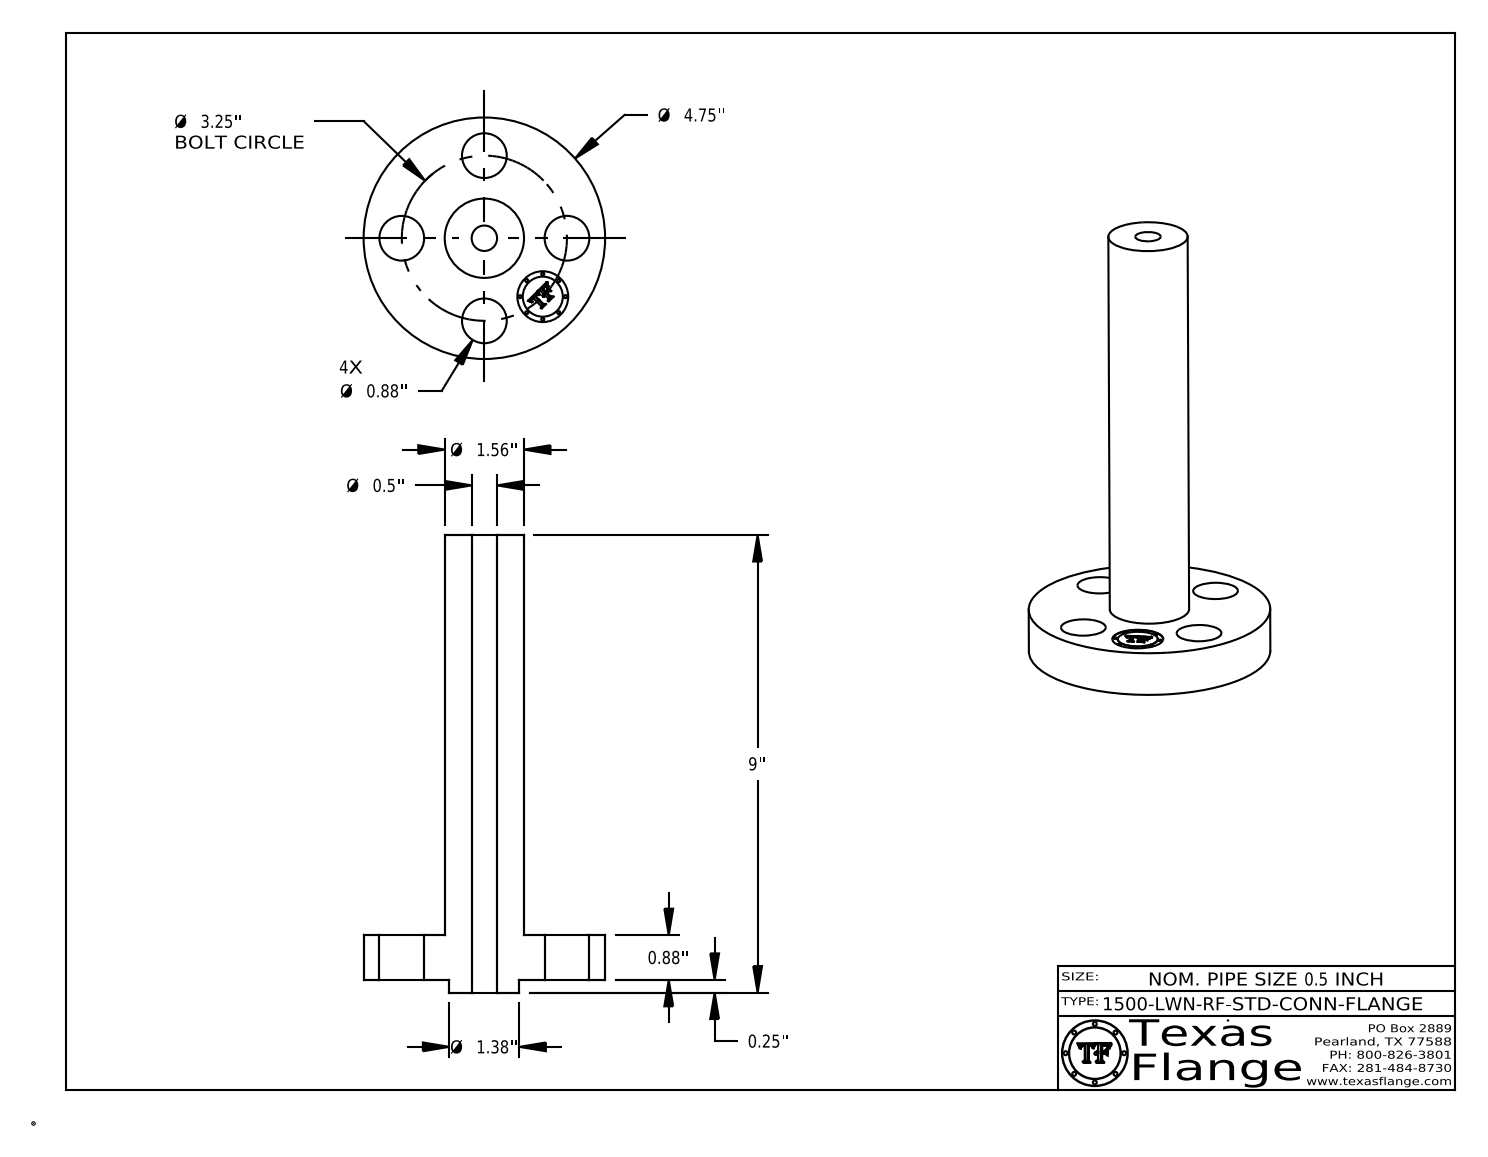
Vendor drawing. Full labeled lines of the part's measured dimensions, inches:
Part name (STEP PRODUCT): 0.5-1500-LWN-RF-STD-CONN-FLANGE
STEP written by: CATIA V5 STEP AP214 (AUTOMOTIVE_DESIGN)
Units: inches
Bodies: 1 solid, 405 faces (369 planar, 36 cylindrical, 0 other)
Overall size (bounding box): 9 × 4.75 × 4.75
Volume: 27.1 in³ · Surface area: 106.9 in²
Round holes (diameter × count): ⌀0.88 ×4, ⌀0.5 ×1, ⌀1 ×1
Round bosses / shafts (diameter × count): ⌀0.061 ×8, ⌀4.75 ×1, ⌀1.56 ×1, ⌀1.38 ×1, ⌀0.788 ×1
Main face-to-face distances: 0.88, 8.75, 7.87, 0.25, 1.13, 9, 1.125, 0.875, 7.875, 0.298
Hole centre spacings: 1.625, 2.298, 1.244, 3.003, 3.25
